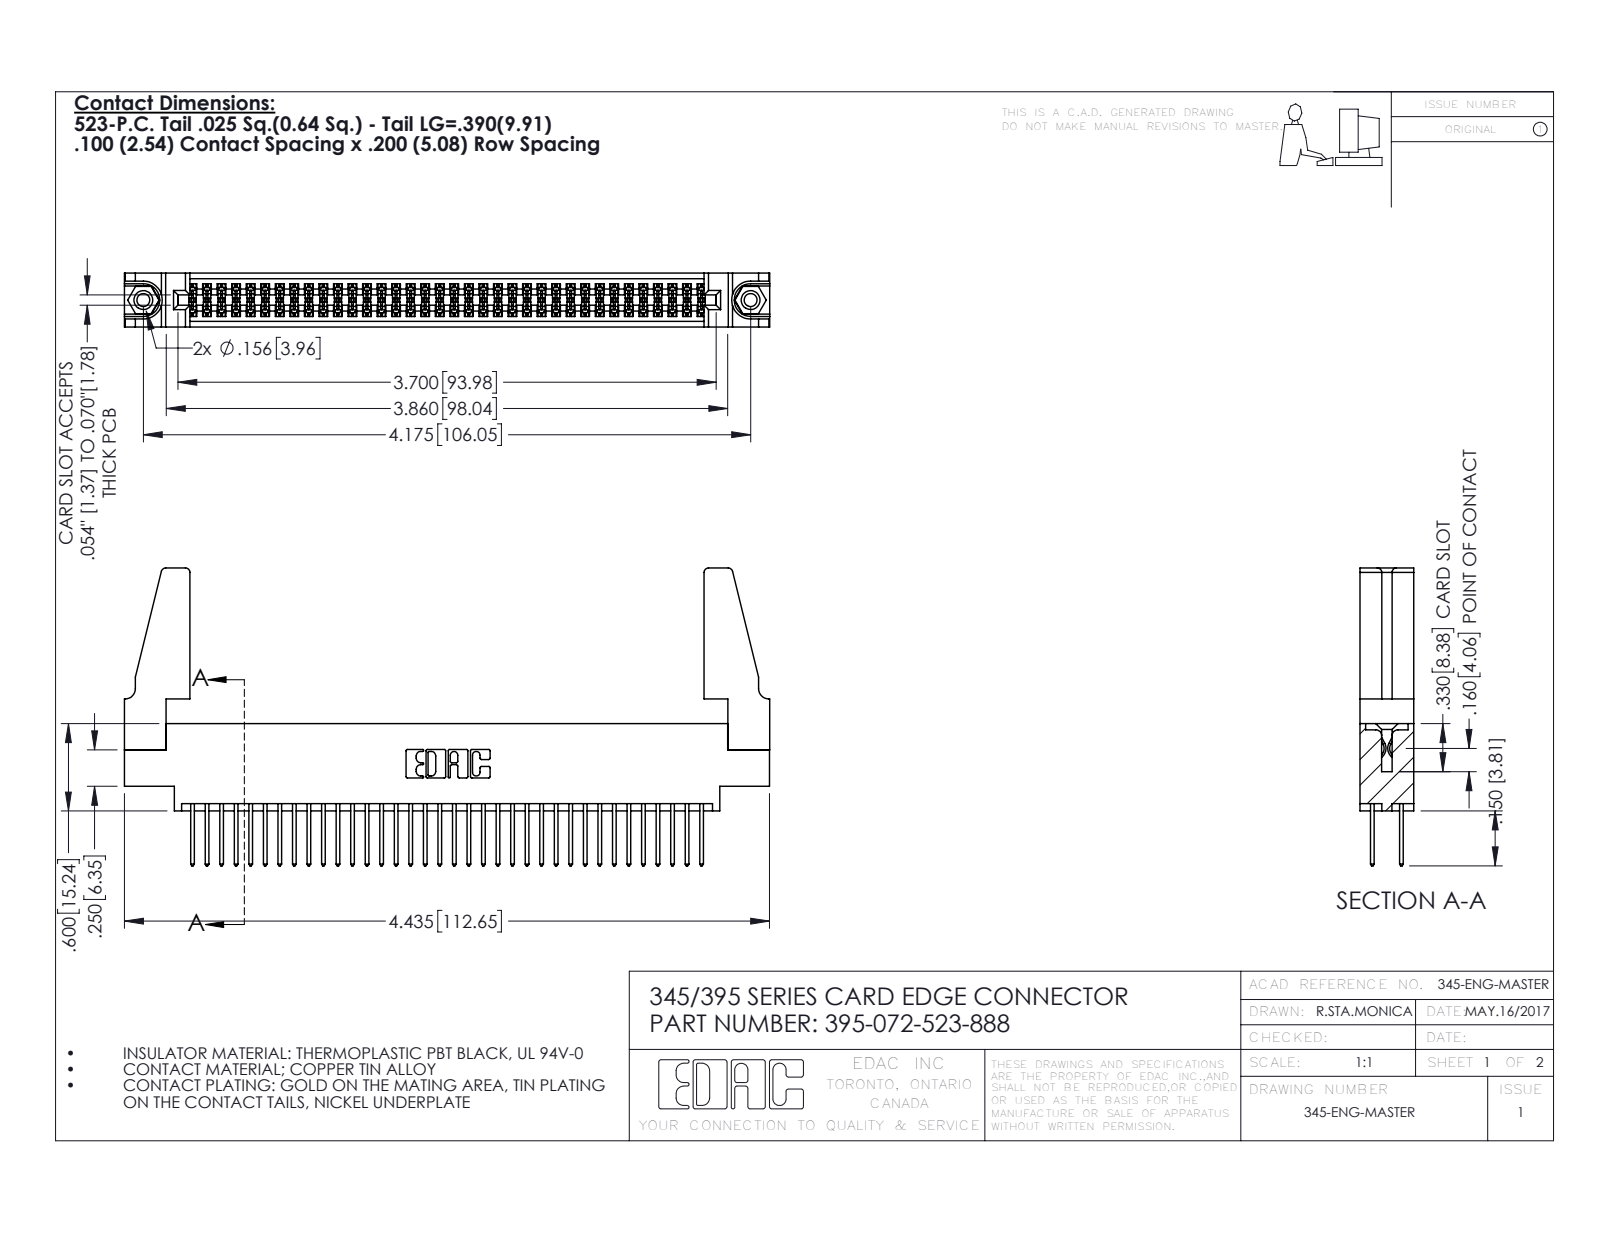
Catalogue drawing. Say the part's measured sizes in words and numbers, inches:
The part is named "345 Part_0.170 Offset - 0.156 Dia-TH; 345-220-078_345-220-088; 395-072-523-888; 345-292-001_345-293-123 (+1 more)". Its 3-D file was written by "SolidWorks 2016 (CONFIG_CONTROL_DESIGN)". It is 77 solids with 3854 faces: 2532 planar, 1306 cylindrical and 16 other. Overall it measures 4.436 by 2.047 by 0.37 inches. Its volume is 0.865 cubic inches and its surface area 30.94 square inches. Round holes: 2 of diameter 0.089, 2 of diameter 0.125, 2 of diameter 0.156, 1 of diameter 0.064. Round bosses or shafts: 2 of diameter 0.155. Partial cylindrical surfaces (rounded edges, fillets, slot ends): 108 of radius 0.006, 72 of radius 0.01, 22 of radius 0.01, 8 of radius 0.03, 6 of radius 0.007, 6 of radius 0.031, 3 of radius 0.026, 2 of radius 0.014. The main face-to-face distances are 0.072, 0.298, 0.37, 0.2, 0.098, 0.272, 0.025, 0.225, 0.175, 0.149. The hole center spacings are 0.27, 3.939, 4.175.
